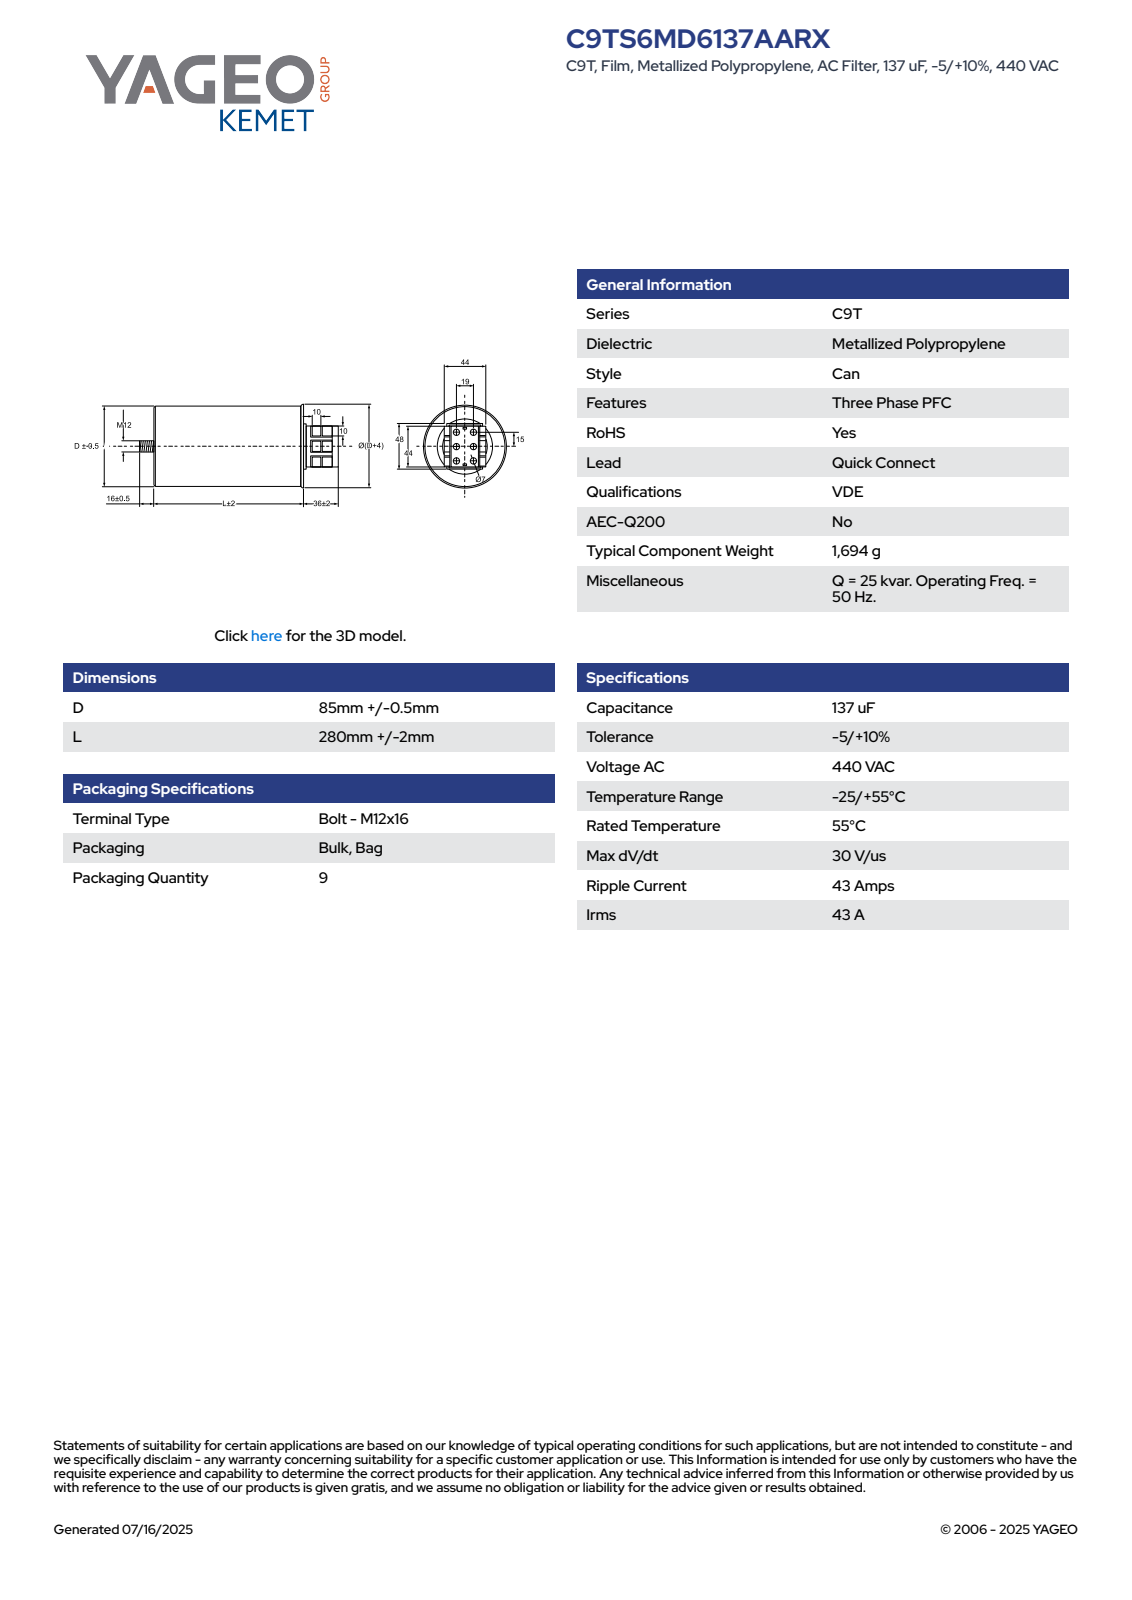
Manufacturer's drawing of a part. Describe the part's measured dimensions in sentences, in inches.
The part is named "CFP_C9T_85X280_D85.5L282". Its 3-D file was written by "SolidWorks 2014 (AUTOMOTIVE_DESIGN)". It is 1 solid with 138 faces: 78 planar, 25 cylindrical and 35 other. Overall it measures 13.248 by 3.524 by 3.524 inches. Its volume is 101.1 cubic inches and its surface area 169.8 square inches. Round holes: 6 of diameter 0.276. Round bosses or shafts: 1 of diameter 3.366, 1 of diameter 0.472. Partial cylindrical surfaces (rounded edges, fillets, slot ends): 1 of radius 1.683. The main face-to-face distances are 0.394, 11.102, 0.439, 0.624, 0.045, 0.157, 1.732, 11.26, 1.496, 0.669. The hole center spacings are 0.591, 0.953, 0.748, 1.181, 1.398.
